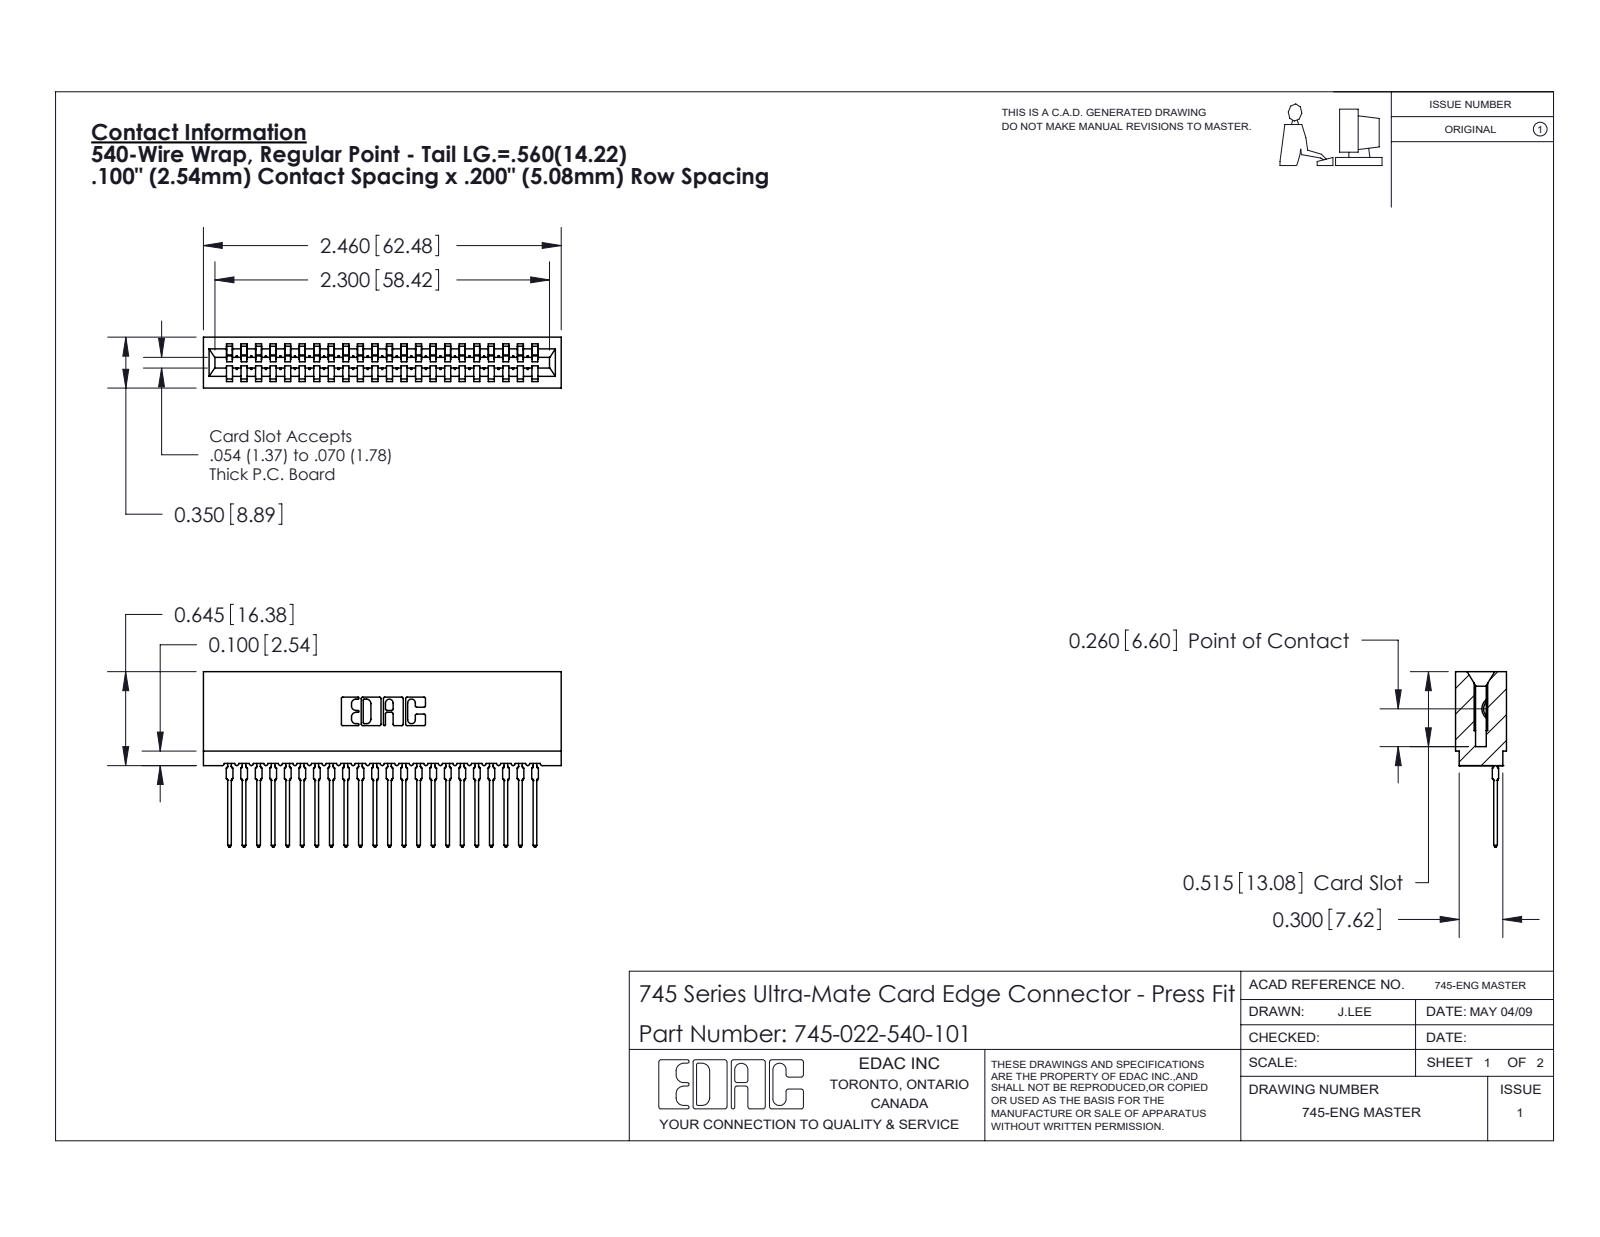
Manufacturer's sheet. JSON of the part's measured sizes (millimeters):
{"part_name": "745-022-540-101; 745 Part_Insulator Option - 01; 745-292-001_540", "step_written_by": "SolidWorks 2020 (CONFIG_CONTROL_DESIGN)", "units": "millimeters", "bodies": {"solids": 23, "faces": 2559, "planar": 1529, "cylindrical": 458, "other": 572}, "overall_size": [62.5, 30.6, 8.9], "volume_mm3": 5600, "surface_area_mm2": 10280, "partial_cylinders_radius": [[0.4, 44], [0.5, 44], [0.3, 22], [0.2, 6], [0.8, 6], [0.1, 4], [0.3, 4], [0.7, 3]], "face_to_face_distances": [2.5, 5.1, 8.9, 3.5, 5.4, 10.2, 7.6, 1.1, 7.7, 2.4]}
